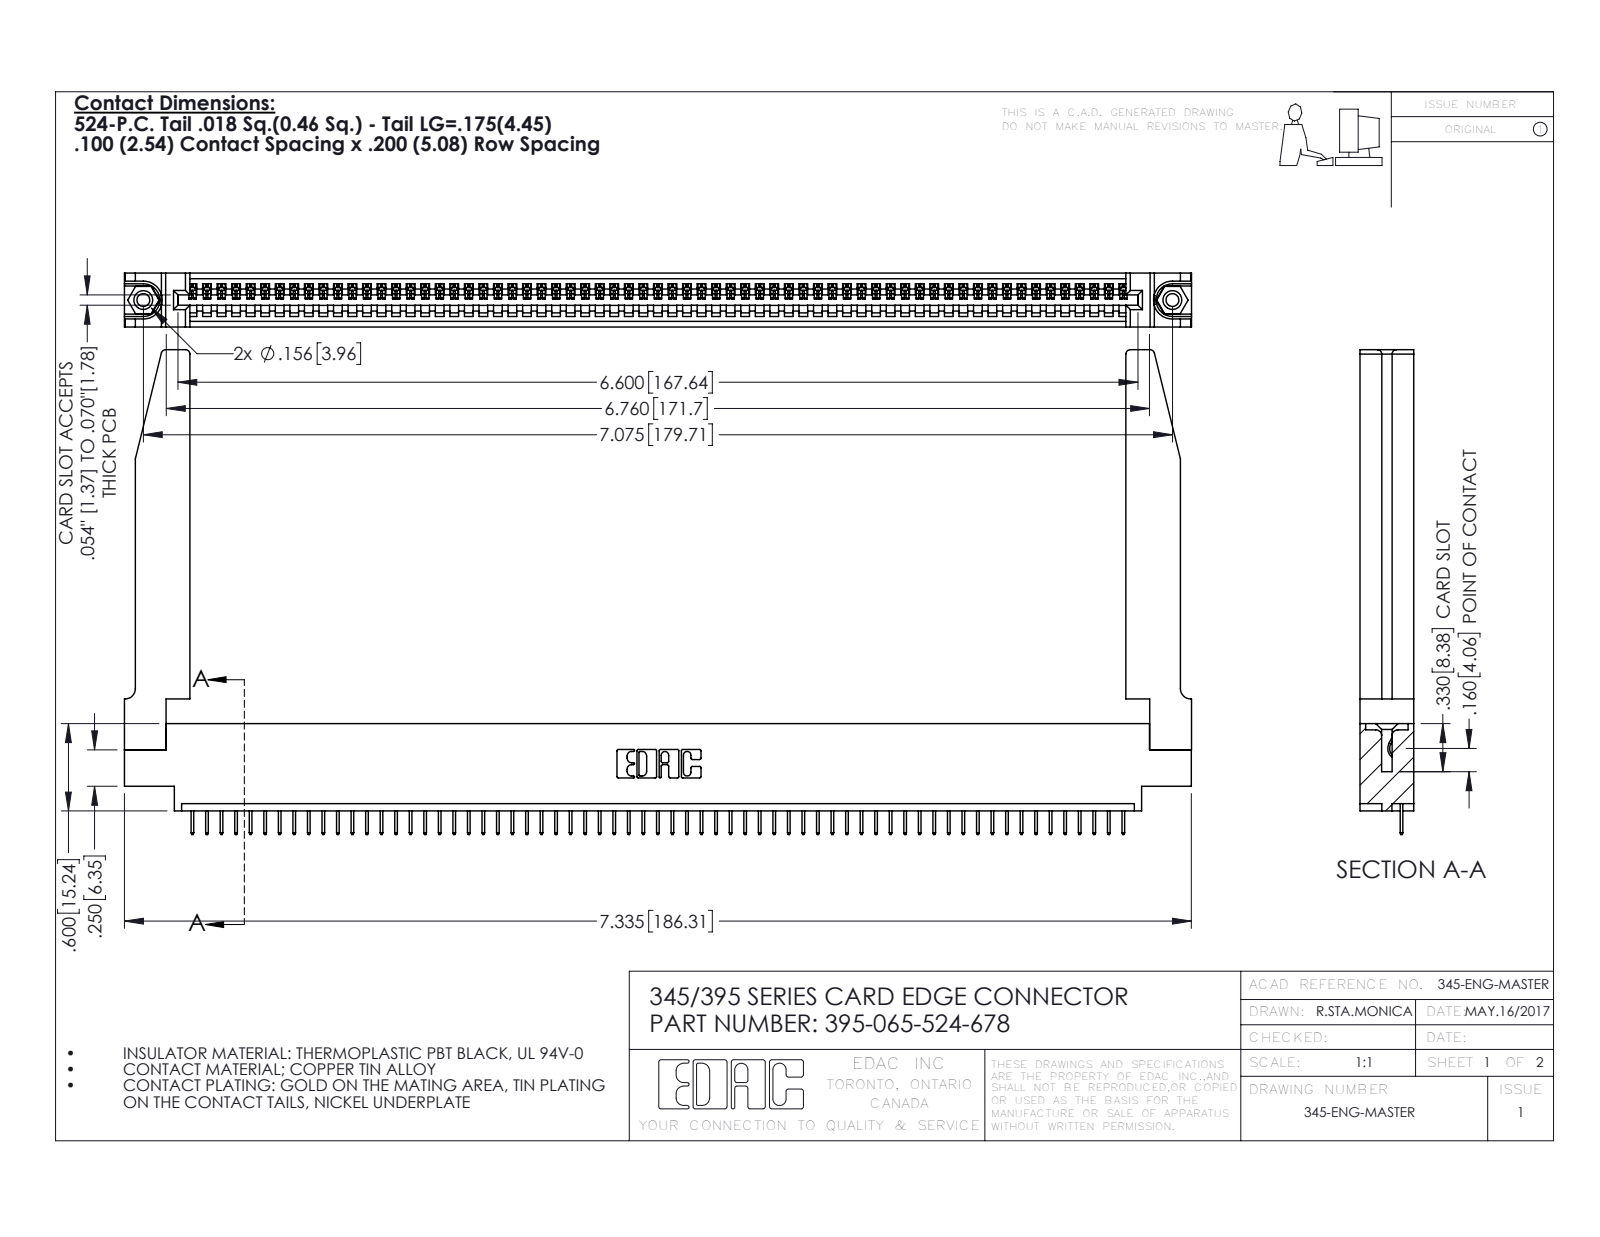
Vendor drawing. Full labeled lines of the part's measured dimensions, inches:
Part name (STEP PRODUCT): 345-250-001_345-250-001-102; 345-292-001_345-293-124; 345 Part_0.170 Offset - 0.156 Dia-TH; 395-065-524-678 (+1 more)
STEP written by: SolidWorks 2016 (CONFIG_CONTROL_DESIGN)
Units: inches
Bodies: 70 solids, 4394 faces (3216 planar, 1126 cylindrical, 52 other)
Overall size (bounding box): 7.336 × 3.332 × 0.37
Volume: 1.543 in³ · Surface area: 46.1 in²
Round holes (diameter × count): ⌀0.089 ×2, ⌀0.125 ×2, ⌀0.156 ×2, ⌀0.064 ×1
Round bosses / shafts (diameter × count): ⌀0.155 ×2
Partial cylindrical surfaces — rounded edges, fillets, slot ends (radius × count): R0.006 ×130, R0.01 ×22, R0.03 ×8, R0.007 ×6, R0.031 ×6, R0.026 ×3, R0.031 ×2, R0.04 ×2
Main face-to-face distances: 0.37, 0.072, 0.298, 0.098, 0.272, 0.025, 0.2, 0.225, 0.072, 0.148
Hole centre spacings: 0.27, 6.839, 7.075
